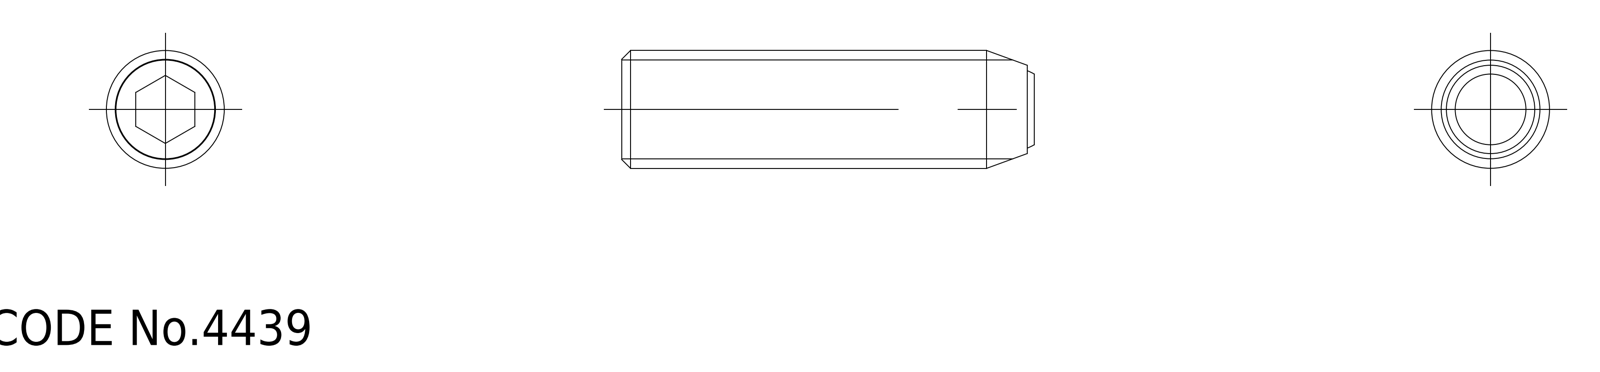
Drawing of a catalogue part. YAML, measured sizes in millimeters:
part_name: "ball; SCS_M10_35_F_15899_36"
step_written_by: "CADfix (AUTOMOTIVE_DESIGN)"
units: millimeters
bodies: {solids: 2, faces: 20, planar: 0, cylindrical: 0, other: 20}
overall_size: [35.73, 10, 10]
volume: 2436
surface_area: 1566
